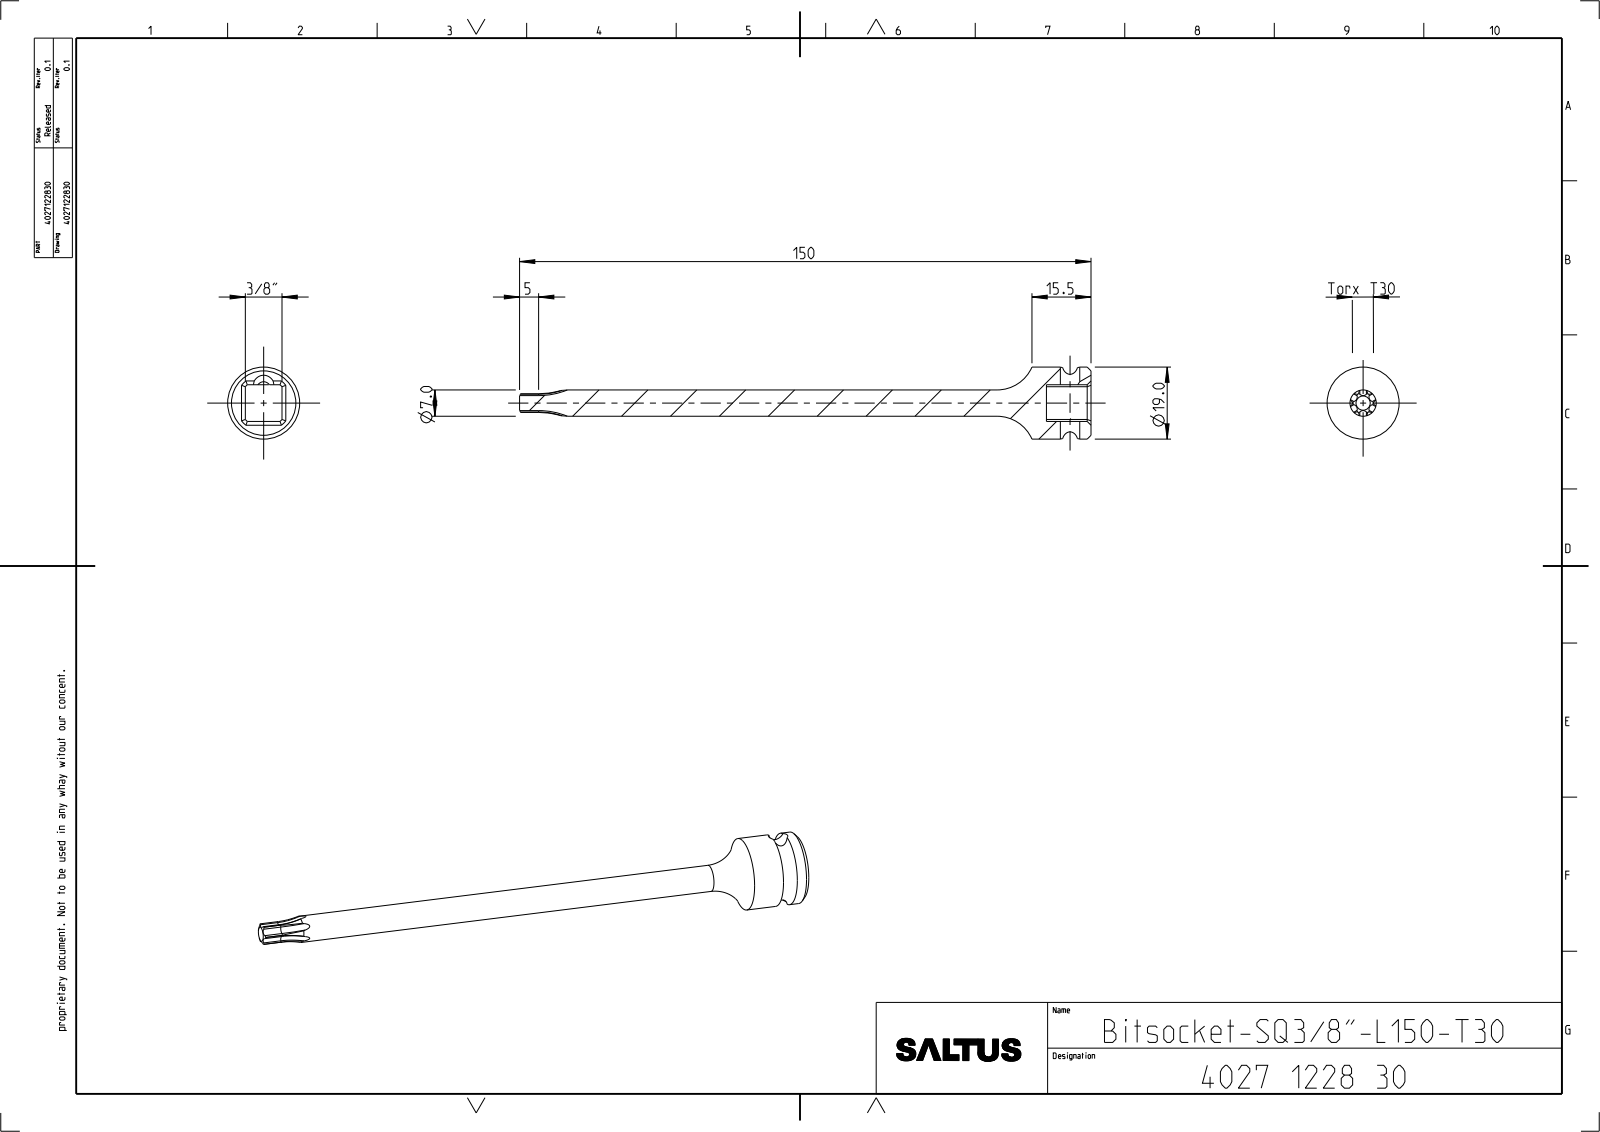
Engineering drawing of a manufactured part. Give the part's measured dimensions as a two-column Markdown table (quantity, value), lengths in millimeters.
| quantity | value |
| --- | --- |
| part name | 4027122830 |
| STEP written by | CREO PARAMETRIC BY PTC INC, 2022414 (CONFIG_CONTROL_DESIGN) |
| units | millimeters |
| bodies | 1 solid, 87 faces (12 planar, 39 cylindrical, 36 other) |
| overall size | 150 × 18.9 × 18.9 |
| volume | 8 149 mm³ |
| surface area | 4 768 mm² |
| round holes (diameter × count) | 5.09 × 1 |
| round bosses / shafts (diameter × count) | 18.9 × 1, 6.9 × 1 |
| partial cylindrical surfaces (radius × count) | 0.42 × 12, 1.22 × 6, 2.76 × 1, 3 × 1, 6.45 × 1 |
| main face-to-face distances | 9.62, 11.7, 150, 138.3 |
